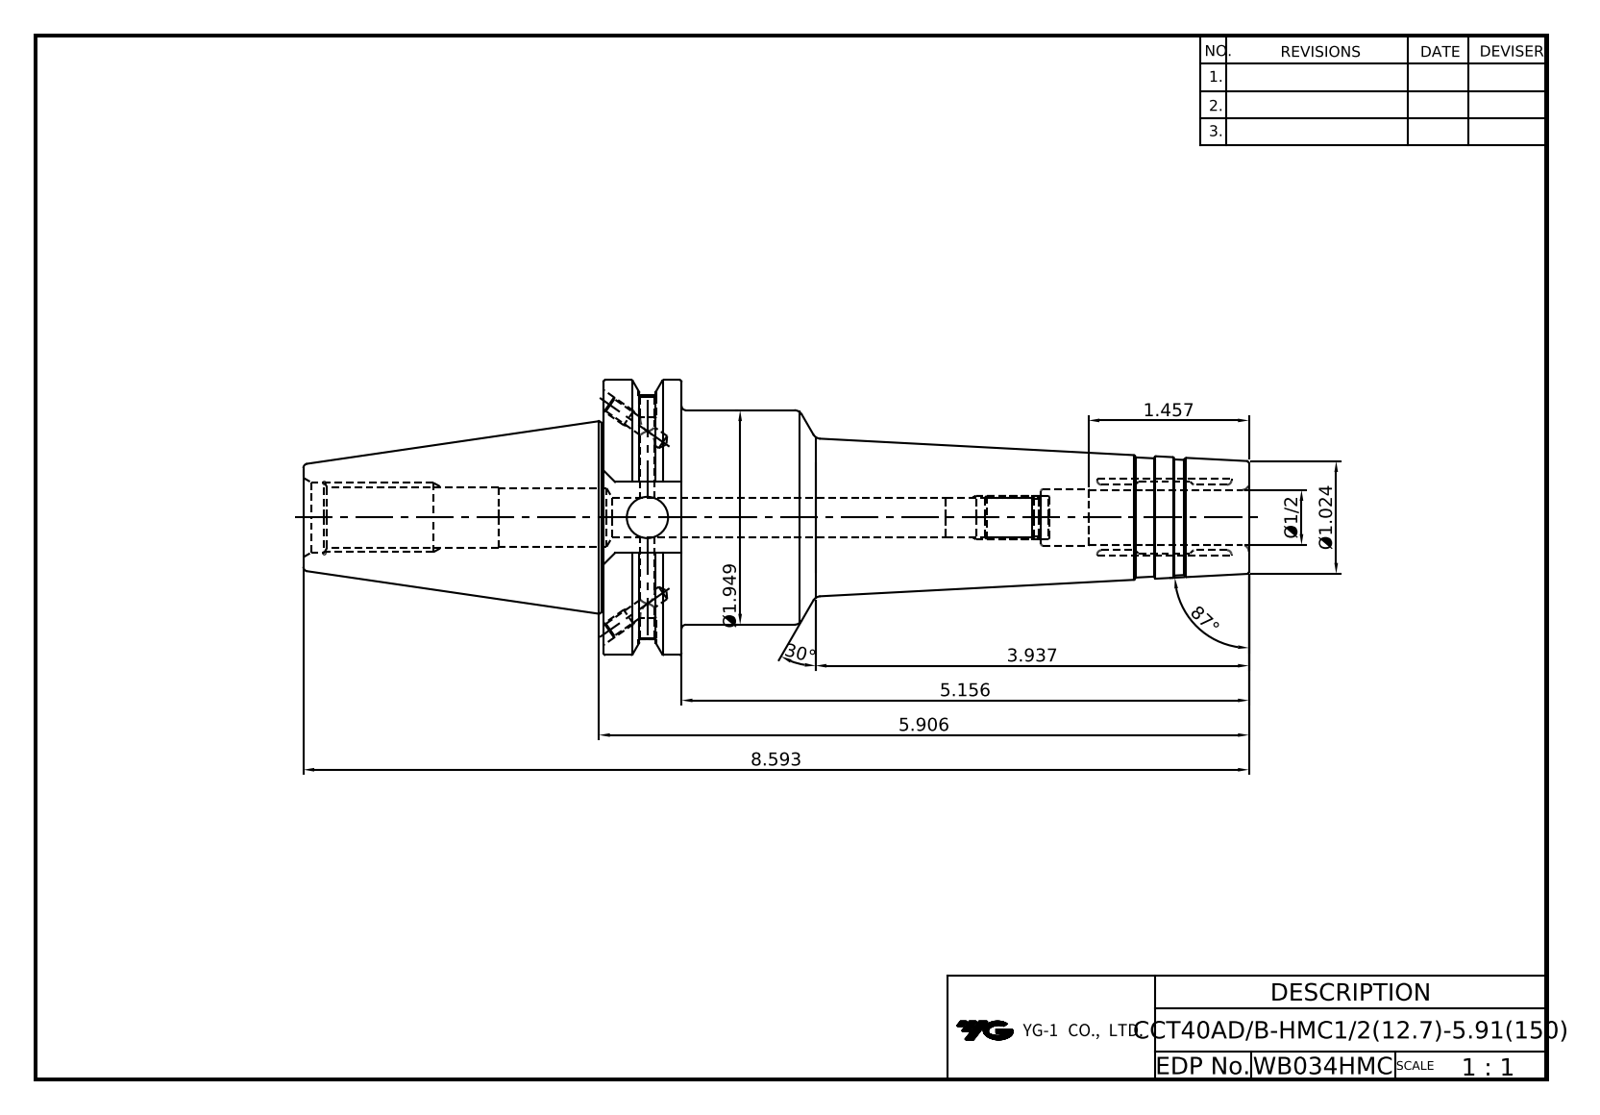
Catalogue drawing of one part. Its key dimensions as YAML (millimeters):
part_name: "LO-CCT40ADB-HMC12.7-150"
step_written_by: "Autodesk Inventor 2025 (AUTOMOTIVE_DESIGN)"
units: millimeters
bodies: {solids: 1, faces: 107, planar: 36, cylindrical: 30, other: 41}
overall_size: [218.25, 63.5, 61.09]
volume: 229330
surface_area: 38510
round_holes:
  - {diameter: 3.24, count: 4}
  - {diameter: 4, count: 2}
  - {diameter: 4.2, count: 2}
  - {diameter: 8, count: 1}
  - {diameter: 8.92, count: 1}
  - {diameter: 9.53, count: 1}
  - {diameter: 12.7, count: 1}
  - {diameter: 13, count: 1}
  - {diameter: 13.2, count: 1}
  - {diameter: 13.39, count: 1}
  - {diameter: 16.3, count: 1}
round_bosses_or_shafts:
  - {diameter: 63.5, count: 1}
  - {diameter: 49.5, count: 1}
partial_cylinders:
  - {radius: 8.19, count: 1}
  - {radius: 28.15, count: 1}
face_to_face_distances: [18.05, 149, 130.95, 47.6, 16.38, 69.25, 87.3, 218.25, 81.3, 12.05]
